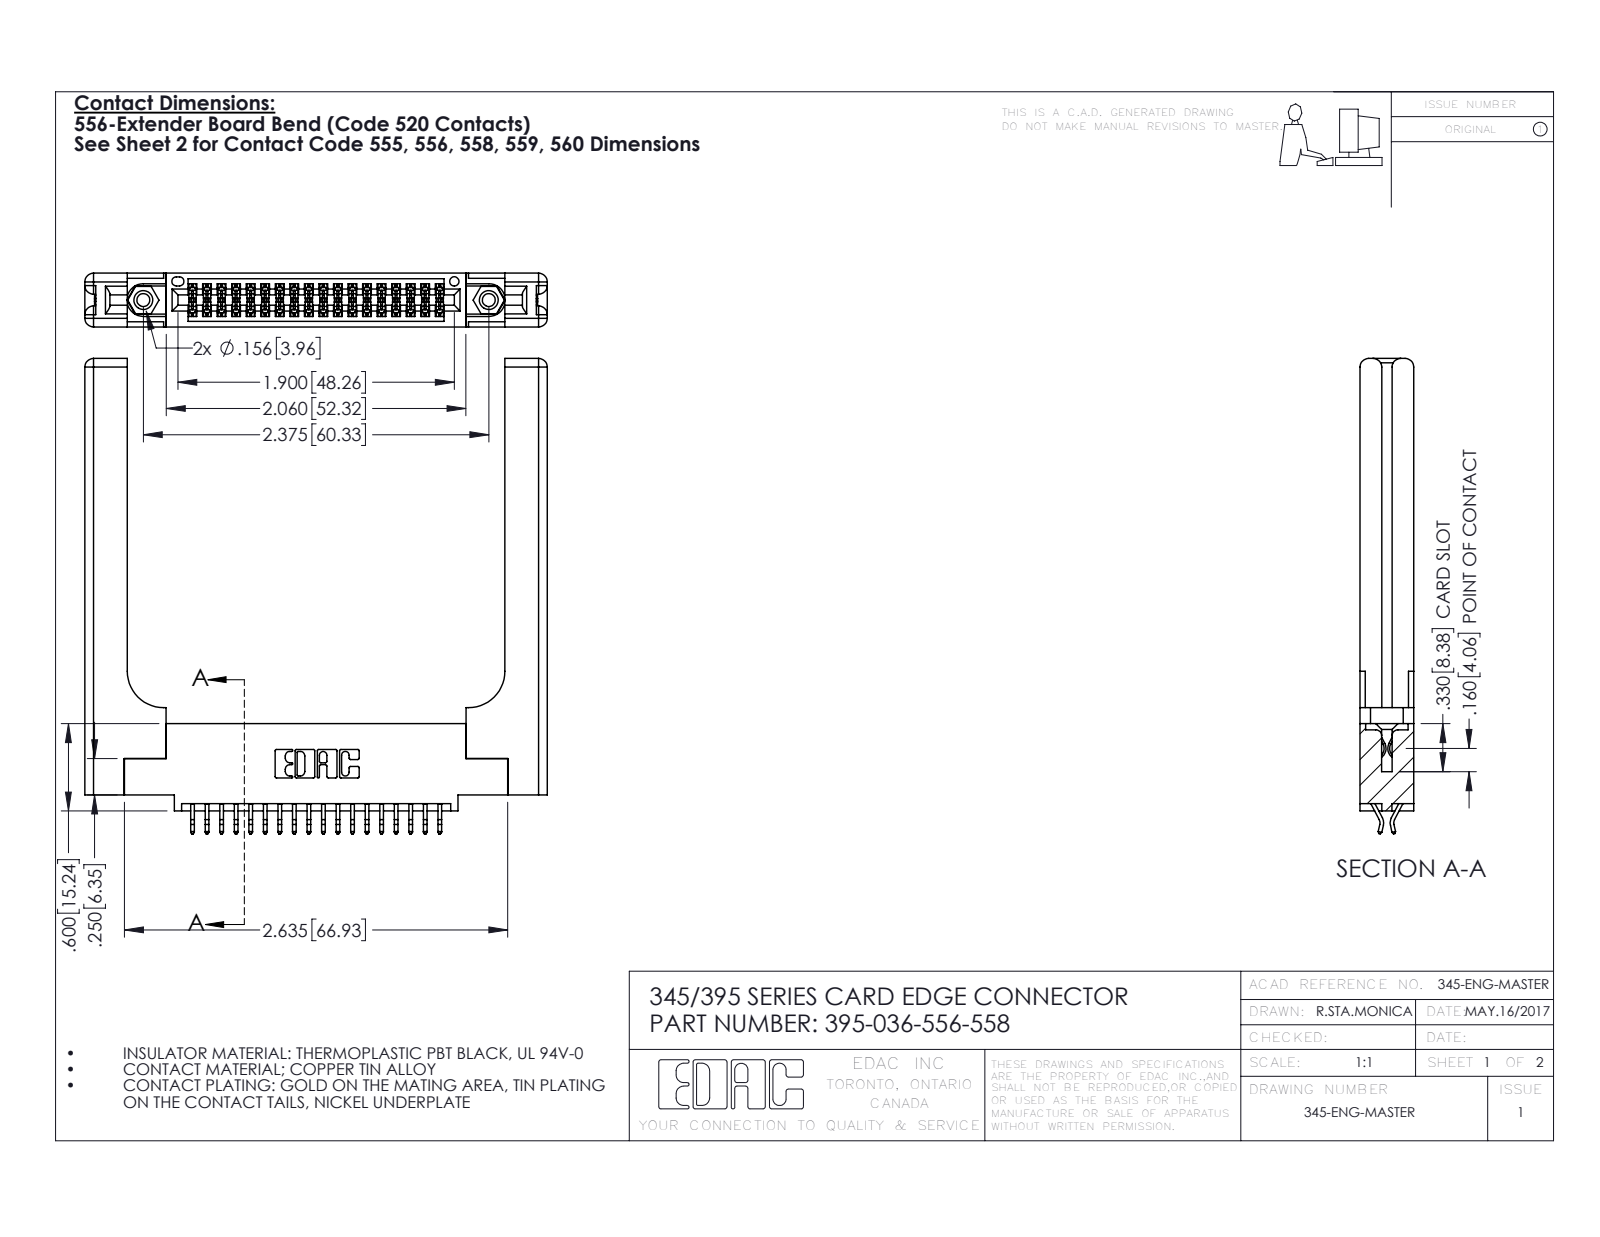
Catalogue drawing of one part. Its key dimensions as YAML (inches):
part_name: "345-250-001_345-250-001-102; 345 Part_0.110 Offset - 0.156 Dia-TH; 395-036-556-558; 345-220-058_345-220-058 (+1 more)"
step_written_by: "SolidWorks 2016 (CONFIG_CONTROL_DESIGN)"
units: inches
bodies: {solids: 41, faces: 2402, planar: 1564, cylindrical: 778, other: 60}
overall_size: [3.267, 3.179, 0.37]
volume: 0.978
surface_area: 24.51
round_holes:
  - {diameter: 0.089, count: 2}
  - {diameter: 0.125, count: 2}
  - {diameter: 0.156, count: 2}
  - {diameter: 0.064, count: 1}
round_bosses_or_shafts:
  - {diameter: 0.155, count: 2}
partial_cylinders:
  - {radius: 0.006, count: 54}
  - {radius: 0.01, count: 22}
  - {radius: 0.06, count: 16}
  - {radius: 0.007, count: 6}
  - {radius: 0.031, count: 6}
  - {radius: 0.026, count: 3}
  - {radius: 0.01, count: 2}
  - {radius: 0.014, count: 2}
face_to_face_distances: [0.37, 0.072, 0.298, 0.148, 0.15, 0.077, 0.22, 0.225, 0.025, 0.098]
hole_center_spacings: [0.27, 2.141, 2.375]
